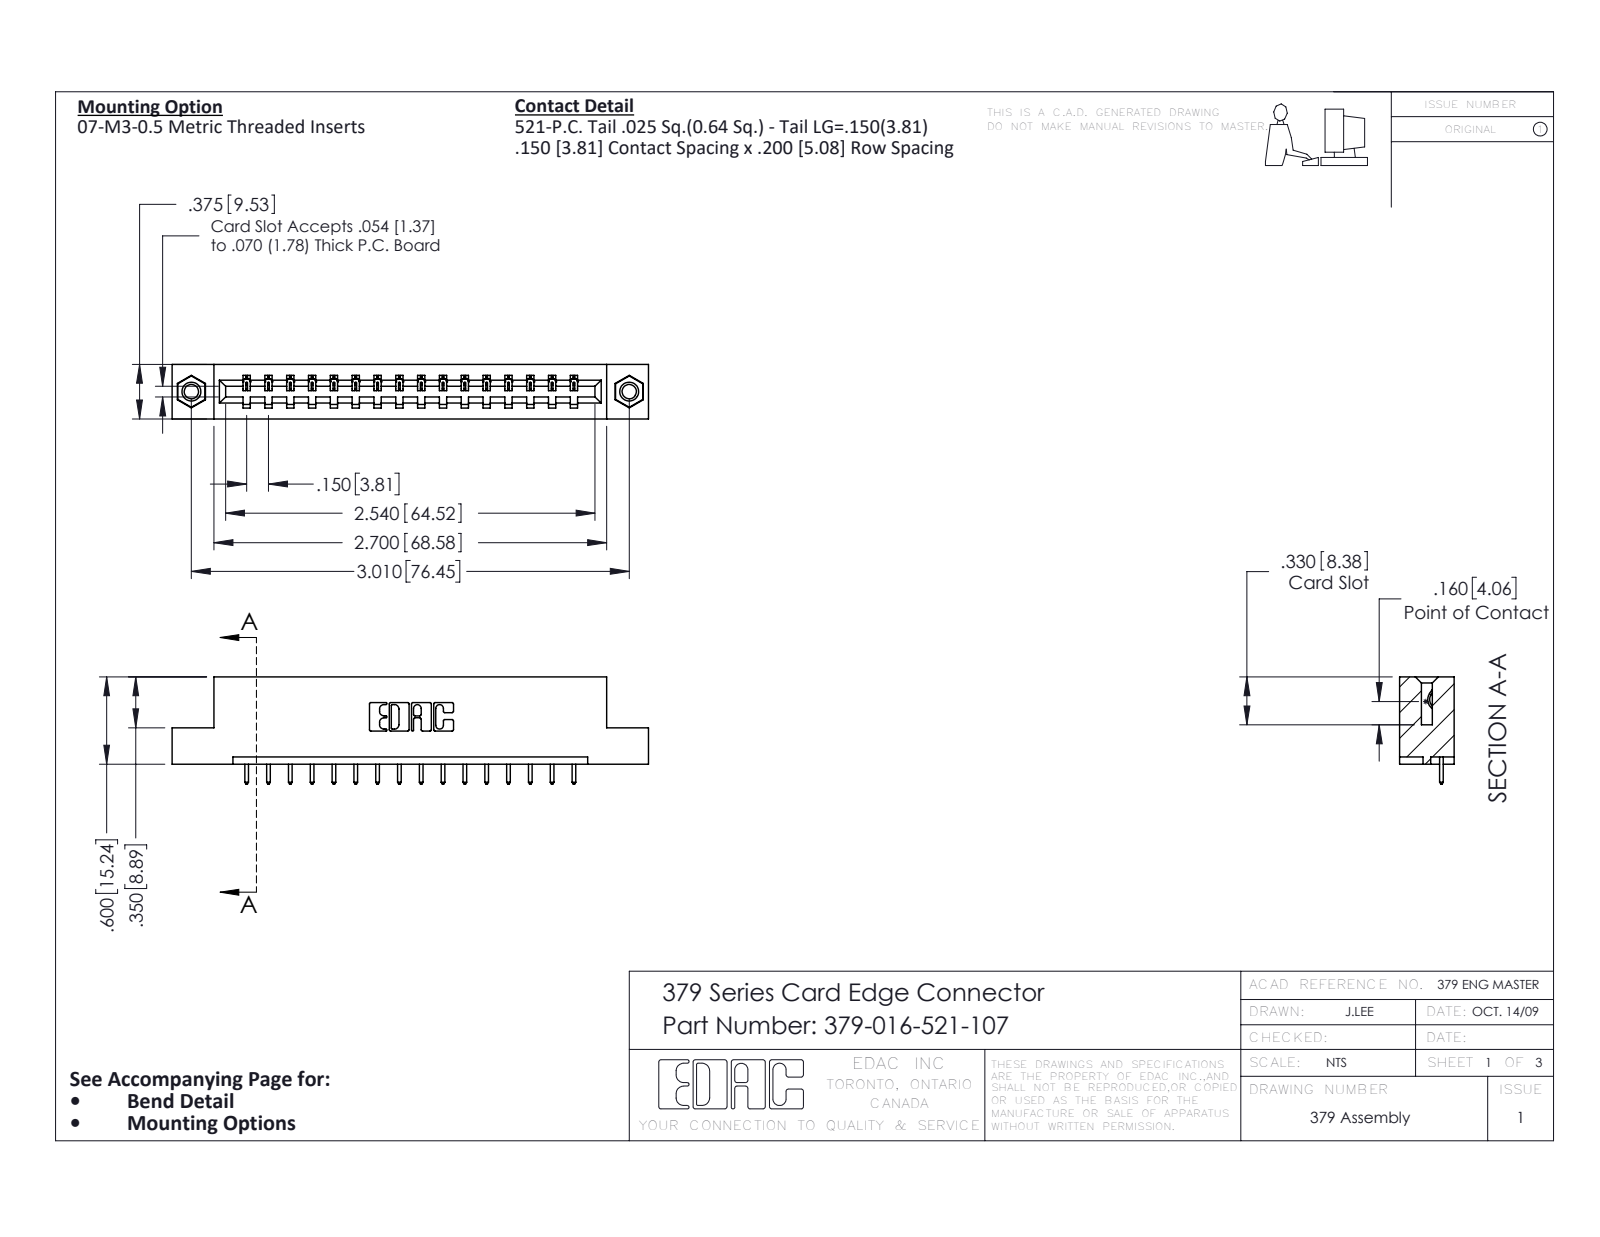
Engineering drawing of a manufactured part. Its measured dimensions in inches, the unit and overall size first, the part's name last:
Units: inches
Overall size (bounding box): 3.275 × 0.737 × 0.375
Round holes (diameter × count): ⌀0.098 ×2, ⌀0.125 ×2, ⌀0.156 ×2
Round bosses / shafts (diameter × count): ⌀0.155 ×2
Partial cylindrical surfaces — rounded edges, fillets, slot ends (radius × count): R0.006 ×32, R0.01 ×32, R0.01 ×22, R0.007 ×6, R0.031 ×6, R0.026 ×3, R0.014 ×1, R0.022 ×1
Main face-to-face distances: 0.3, 0.075, 0.375, 0.6, 0.15, 0.225, 0.45, 0.2, 0.75, 0.9
Hole centre spacings: 3.01
Volume: 0.511 in³ · Surface area: 12.84 in²
Bodies: 19 solids, 1102 faces (774 planar, 312 cylindrical, 16 other)
Part name (STEP PRODUCT): 379-016-521-107; 379 Part_Flush - .156 Dia - TI; 345-250-001_345-250-005-103; 345-292-001_345-293-121
STEP written by: SolidWorks 2020 (CONFIG_CONTROL_DESIGN)
